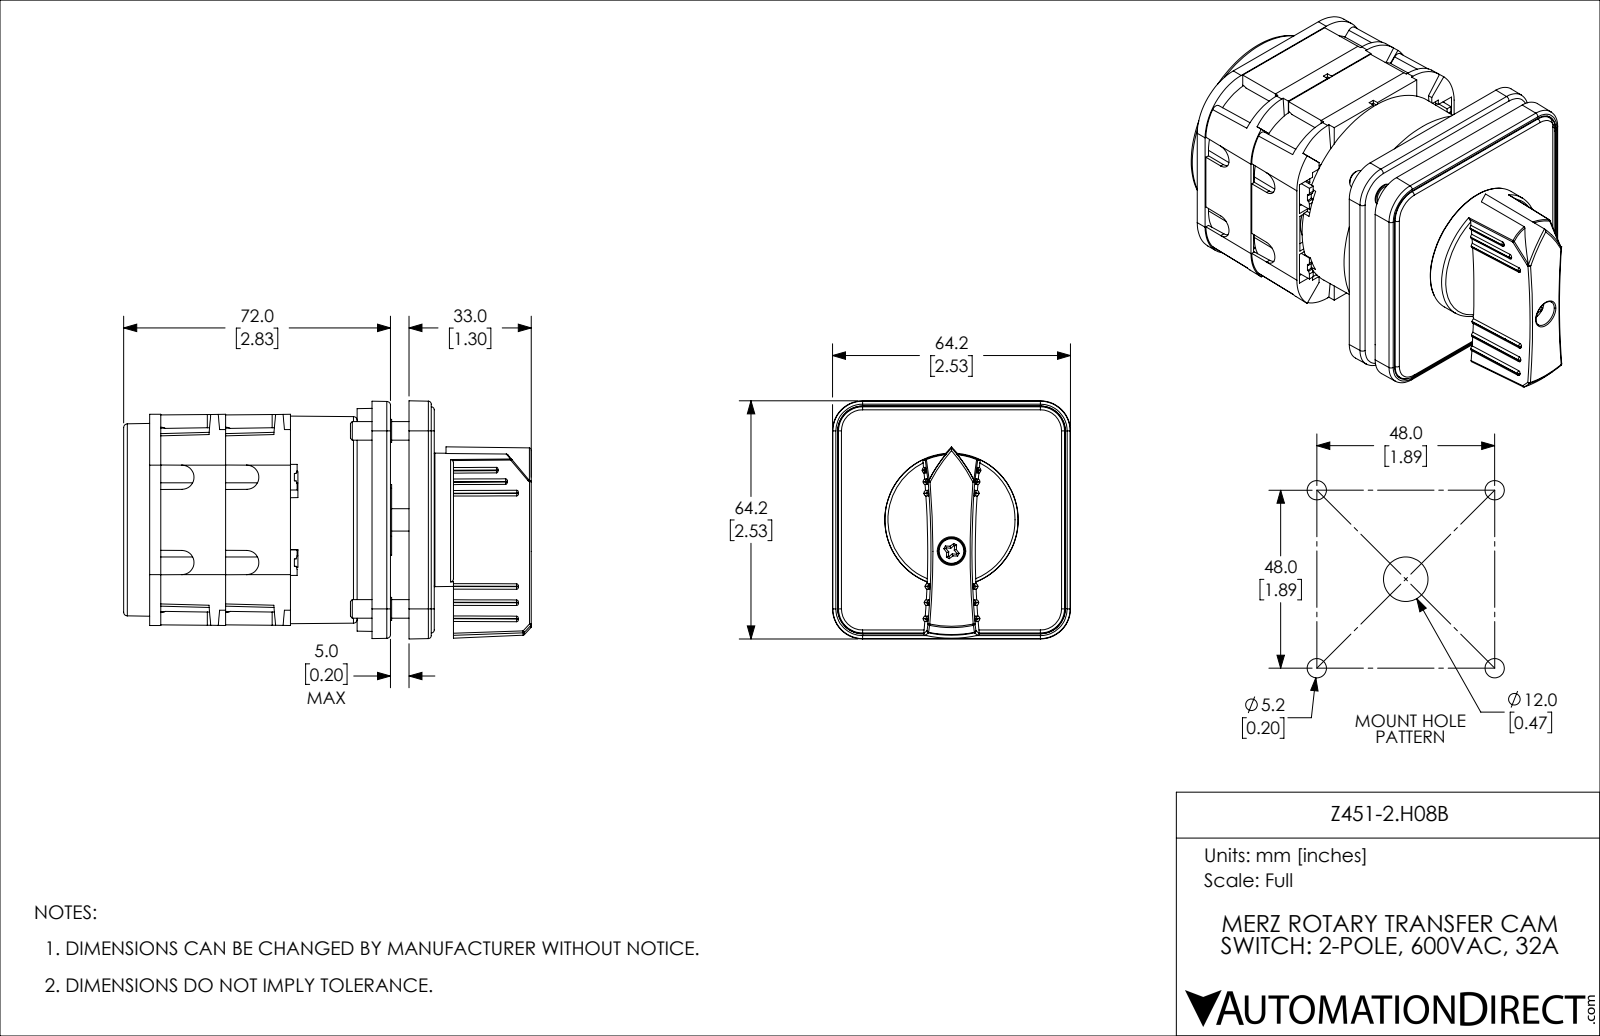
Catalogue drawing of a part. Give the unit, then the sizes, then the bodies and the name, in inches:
Units: inches
Overall size (bounding box): 4.331 × 2.528 × 2.528
Round holes (diameter × count): ⌀0.315 ×6, ⌀0.012 ×4, ⌀0.157 ×4, ⌀0.197 ×4, ⌀0.205 ×4, ⌀0.374 ×4, ⌀0.24 ×2, ⌀0.394 ×1, ⌀0.512 ×1, ⌀0.551 ×1, ⌀0.925 ×1
Round bosses / shafts (diameter × count): ⌀0.197 ×5, ⌀0.366 ×4, ⌀0.319 ×4, ⌀0.287 ×4, ⌀0.622 ×1, ⌀0.413 ×1
Partial cylindrical surfaces — rounded edges, fillets, slot ends (radius × count): R0.008 ×14, R0.039 ×13, R0.031 ×11, R0.02 ×6, R0.169 ×6, R0.006 ×4, R0.018 ×4, R0.098 ×4
Main face-to-face distances: 0.098, 0.394, 0.748, 0.689, 1.457, 0.071, 0.465, 0.717, 0.197, 0.591
Hole centre spacings: 0.802, 1.67, 0.334, 0.355, 0.368, 0.374, 0.644, 0.648
Volume: 12.66 in³ · Surface area: 153.3 in²
Bodies: 12 solids, 2897 faces (1679 planar, 247 cylindrical, 971 other)
Part name (STEP PRODUCT): Z451-2.H08B
STEP written by: SolidWorks 2019 (AUTOMOTIVE_DESIGN)
